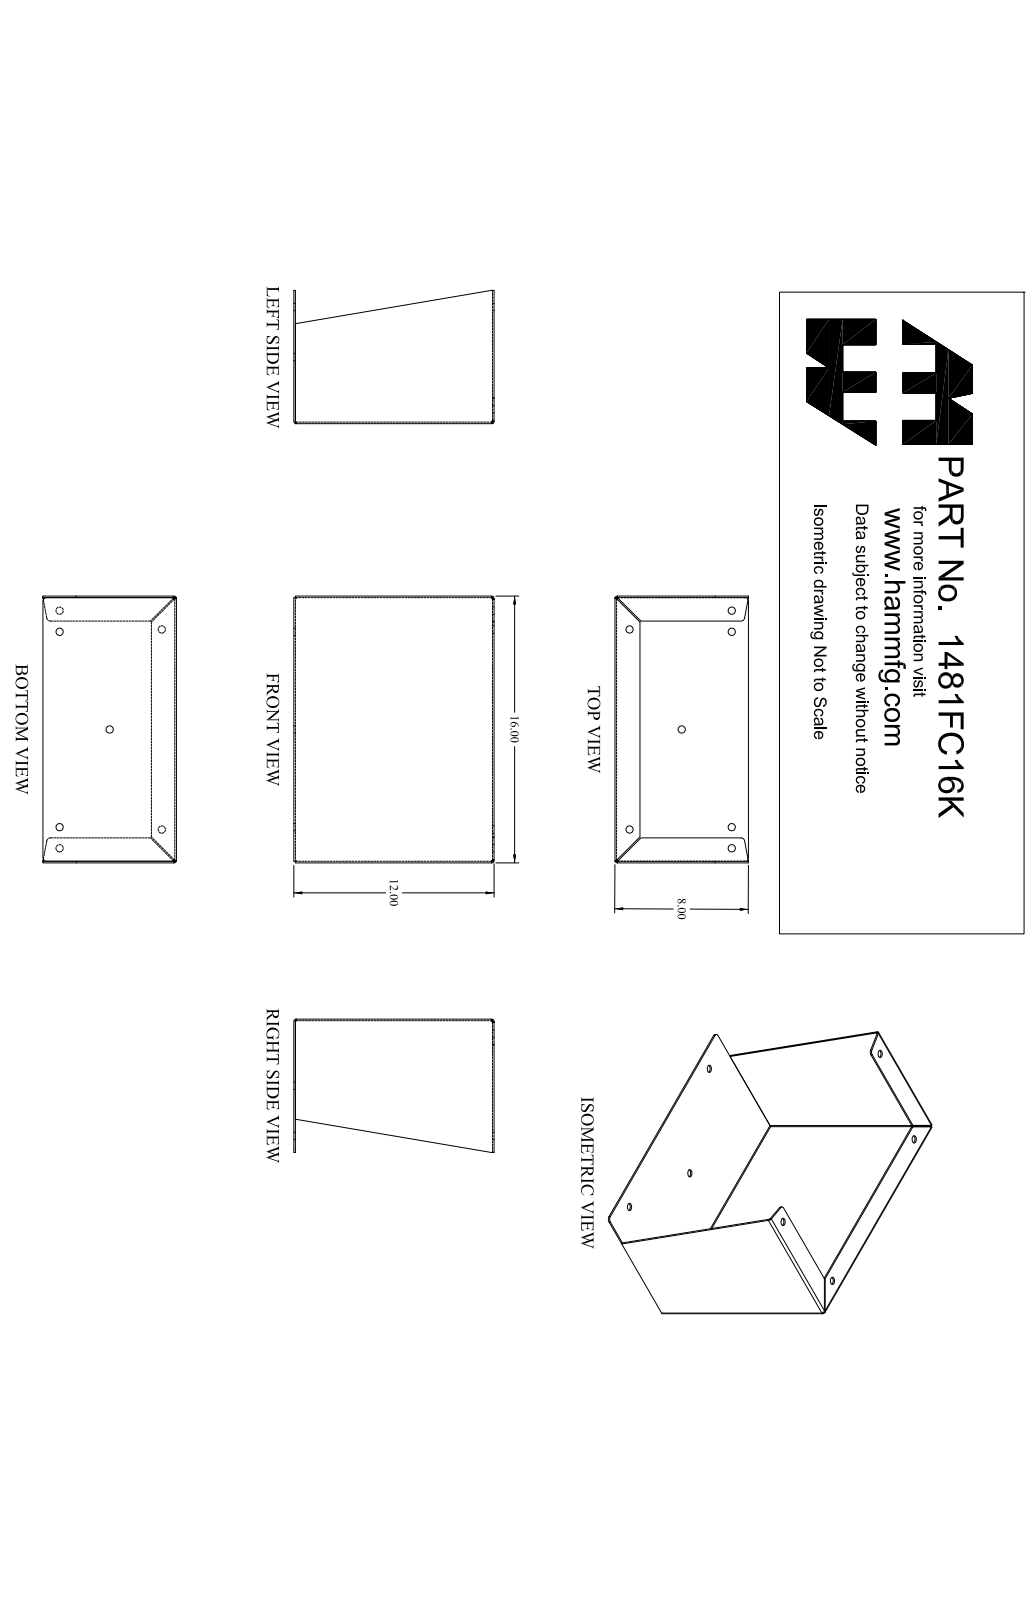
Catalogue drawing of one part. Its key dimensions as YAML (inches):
part_name: "1481FC16K_Default"
step_written_by: "SolidWorks 2019 (CONFIG_CONTROL_DESIGN)"
units: inches
bodies: {solids: 1, faces: 78, planar: 42, cylindrical: 30, other: 6}
overall_size: [16, 12, 8]
volume: 49.15
surface_area: 1046
round_holes:
  - {diameter: 0.437, count: 7}
partial_cylinders:
  - {radius: 0.048, count: 6}
  - {radius: 0.143, count: 6}
  - {radius: 0.22, count: 4}
face_to_face_distances: [0.095, 15.905, 0.095, 16, 15.81, 11.81, 11.905, 11.905, 12, 1.405]
hole_center_spacings: [6.126, 6.227, 6.582, 6.765, 13.347, 1.266, 1.266, 7.731]
